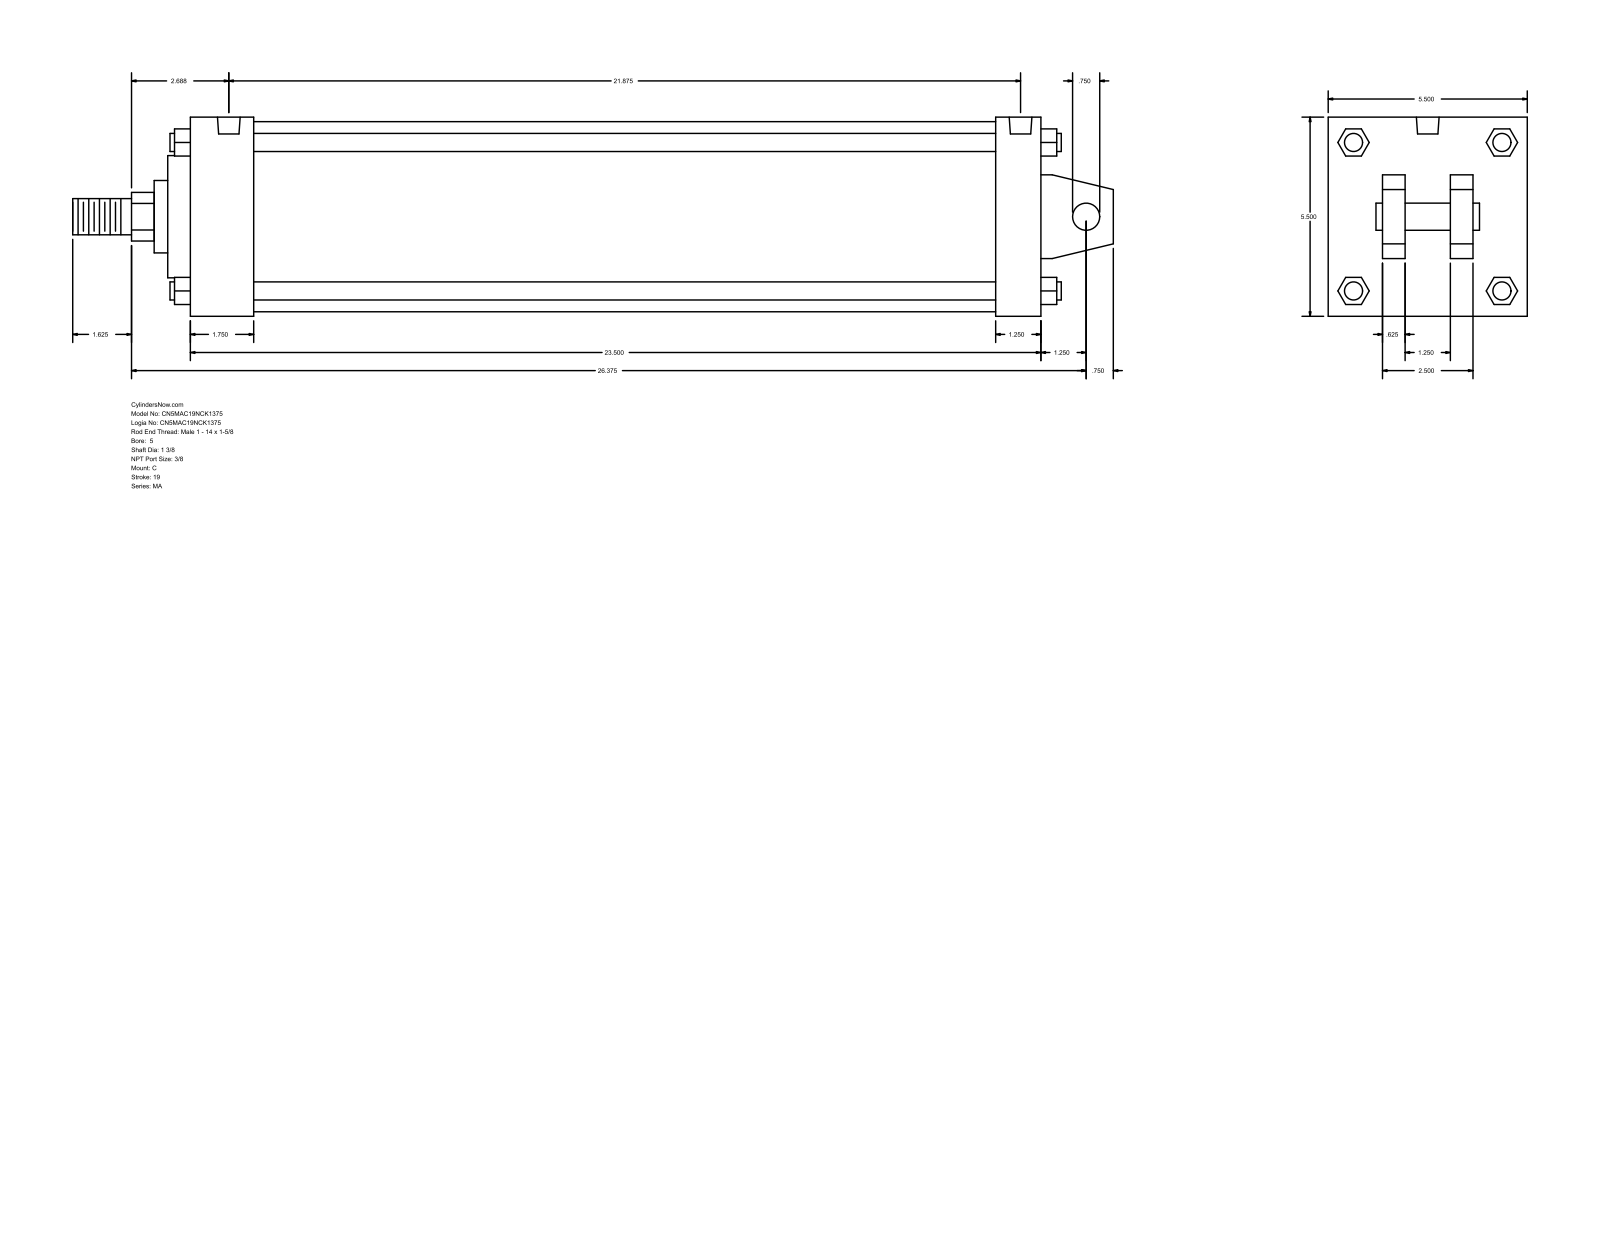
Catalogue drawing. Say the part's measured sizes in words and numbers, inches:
The part is named "MA_C__0500_1.375". Its 3-D file was written by "GSSL Pune (CONFIG_CONTROL_DESIGN)". It is 0 solids with 141 faces: 109 planar, 32 cylindrical and 0 other. Overall it measures 28.75 by 5.5 by 5.5 inches. Round holes: 4 of diameter 0.437, 2 of diameter 0.627. Round bosses or shafts: 4 of diameter 0.5, 1 of diameter 5.25, 1 of diameter 3.375, 1 of diameter 2, 1 of diameter 1.375, 1 of diameter 1, 1 of diameter 0.75. Partial cylindrical surfaces (rounded edges, fillets, slot ends): 1 of radius 0.672. The main face-to-face distances are 5.5, 23.5, 0.625, 22.25, 1.25, 1.75, 20.5, 21.75, 2.125, 1.5. The hole center spacings are 0.188, 21.5, 21.687, 21.875.
